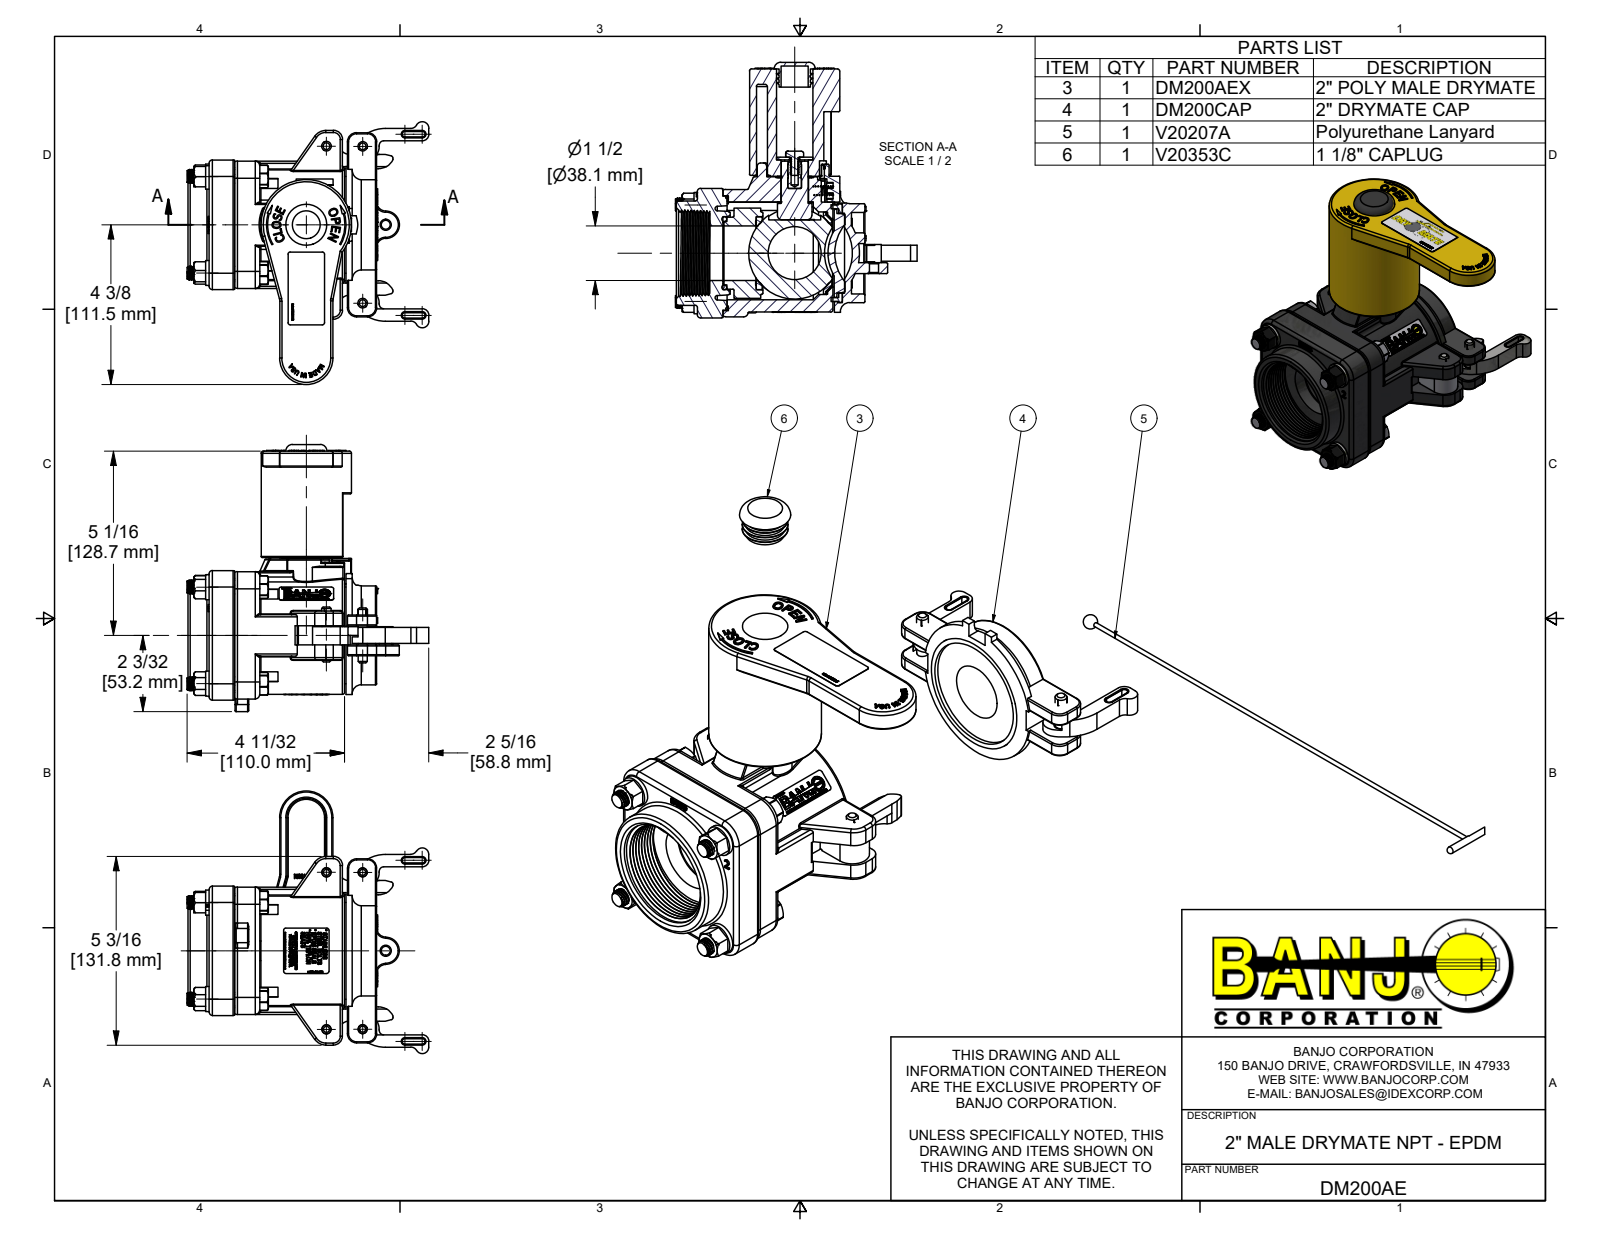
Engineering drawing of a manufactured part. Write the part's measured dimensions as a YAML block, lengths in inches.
part_name: "DM200AE; DM200AEX; DM20254; DM20254MY (+8 more)"
step_written_by: "Autodesk Inventor 2022 (AUTOMOTIVE_DESIGN)"
units: inches
bodies: {solids: 46, faces: 6043, planar: 2877, cylindrical: 890, other: 2276}
overall_size: [7.34, 7.22, 6.646]
volume: 49.82
surface_area: 430.3
round_holes:
  - {diameter: 0.25, count: 5}
  - {diameter: 0.375, count: 5}
  - {diameter: 0.256, count: 4}
  - {diameter: 0.307, count: 4}
  - {diameter: 0.385, count: 4}
  - {diameter: 0.406, count: 4}
  - {diameter: 0.42, count: 4}
  - {diameter: 0.125, count: 3}
  - {diameter: 0.196, count: 1}
  - {diameter: 0.2, count: 1}
  - {diameter: 0.227, count: 1}
  - {diameter: 0.281, count: 1}
round_bosses_or_shafts:
  - {diameter: 0.324, count: 60}
  - {diameter: 0.687, count: 4}
  - {diameter: 0.375, count: 4}
  - {diameter: 0.26, count: 4}
  - {diameter: 0.249, count: 4}
  - {diameter: 0.28, count: 3}
  - {diameter: 2.48, count: 2}
  - {diameter: 3.25, count: 1}
partial_cylinders:
  - {radius: 0.03, count: 104}
  - {radius: 0.06, count: 52}
  - {radius: 0.02, count: 20}
  - {radius: 0.01, count: 12}
  - {radius: 0.125, count: 10}
  - {radius: 0.25, count: 10}
  - {radius: 0.09, count: 8}
  - {radius: 0.162, count: 8}
face_to_face_distances: [3.53, 0.298, 2.91, 3.725, 0.035, 0.297, 0.03, 0.25, 0.822, 3.28]
hole_center_spacings: [2.653, 1.872, 1.88, 2.648, 2.658, 3.752, 0.95, 1.646]
